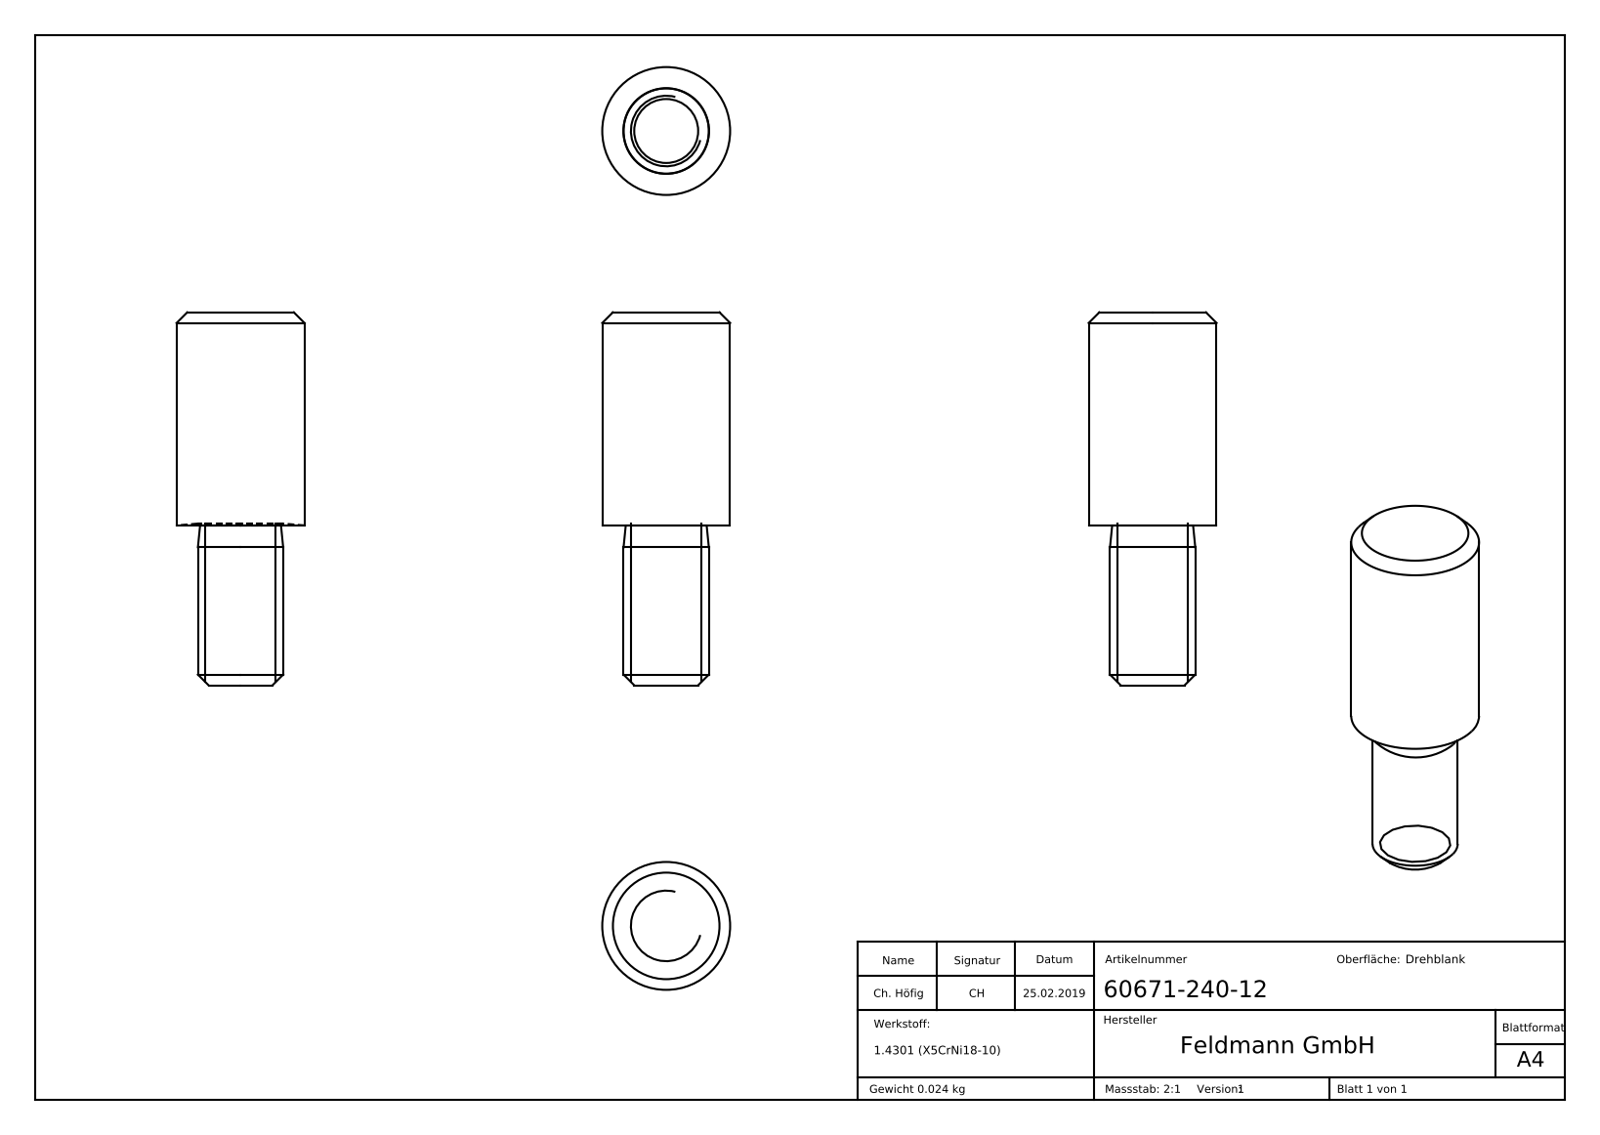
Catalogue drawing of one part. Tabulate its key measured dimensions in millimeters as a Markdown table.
| quantity | value |
| --- | --- |
| part name | 60671-240-12 |
| STEP written by | SolidWorks 2015 (CONFIG_CONTROL_DESIGN) |
| units | millimeters |
| bodies | 1 solid, 253 faces (141 planar, 4 cylindrical, 108 other) |
| overall size | 35 × 12 × 12 |
| volume | 2 976 mm³ |
| surface area | 1 326 mm² |
| round bosses / shafts (diameter × count) | 12 × 1, 8 × 1 |
| main face-to-face distances | 35, 34.9, 0.65, 1.44, 0.92, 0.68, 0.57, 1.3, 0.33, 1.68 |
